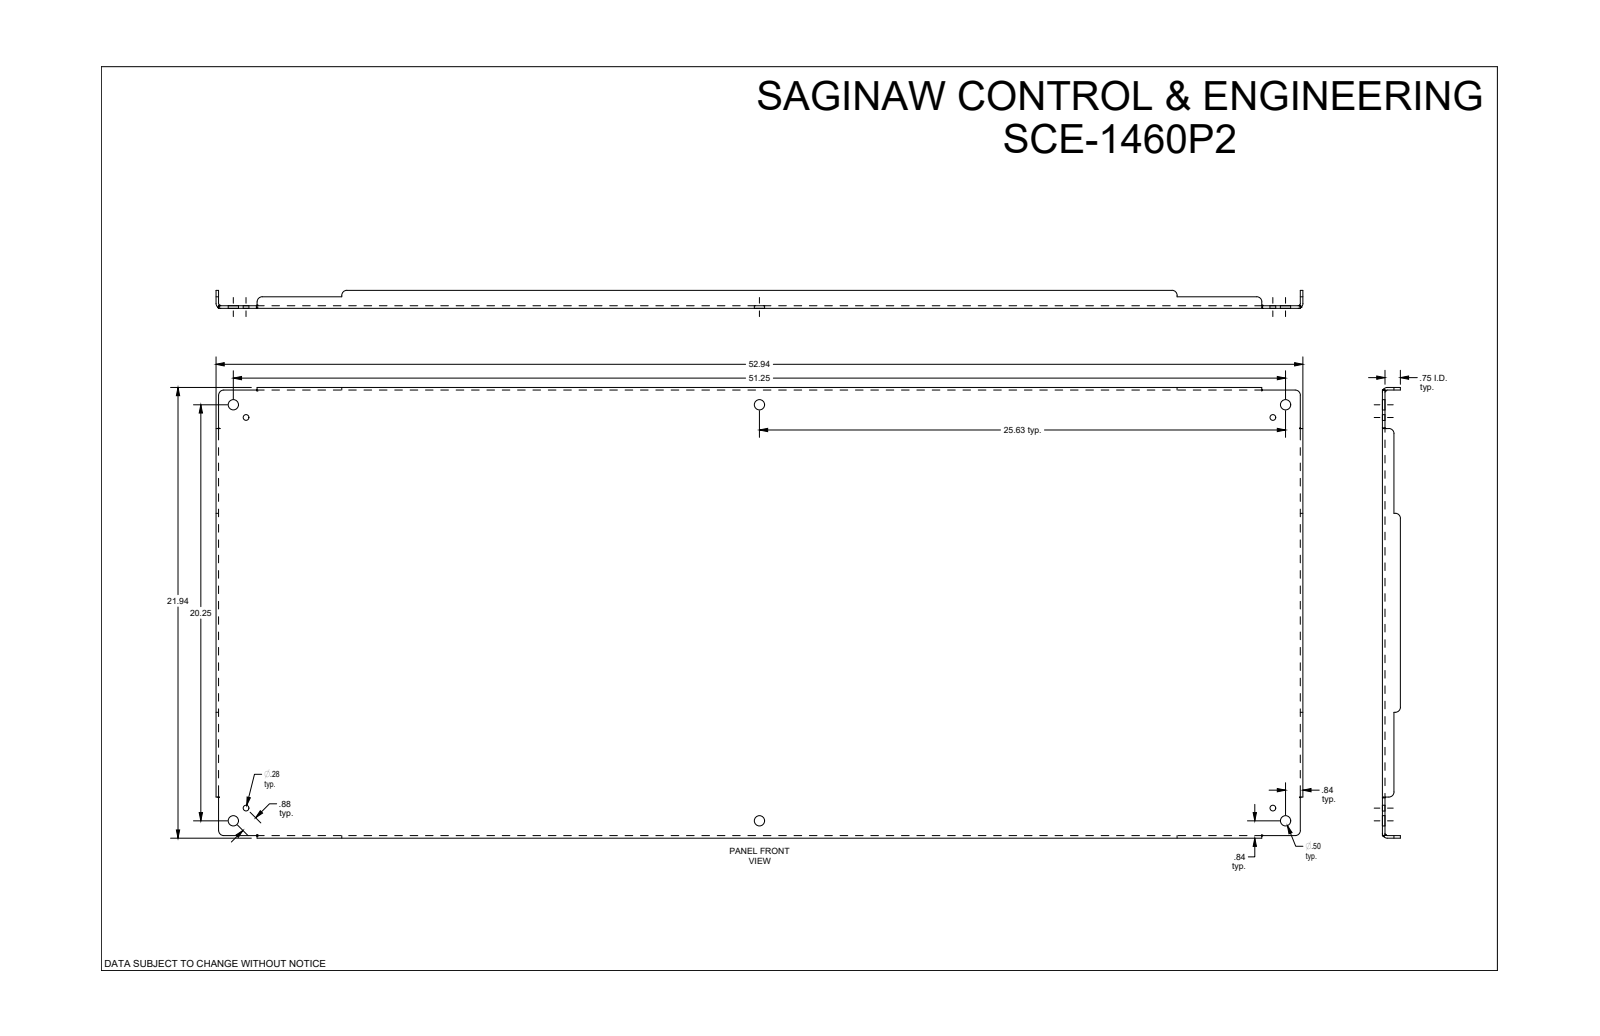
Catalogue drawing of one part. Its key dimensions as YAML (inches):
part_name: "SCE-1460P2"
step_written_by: "SolidWorks 2019 (CONFIG_CONTROL_DESIGN)"
units: inches
bodies: {solids: 1, faces: 108, planar: 46, cylindrical: 38, other: 24}
overall_size: [52.938, 21.938, 0.875]
volume: 154.7
surface_area: 2496
round_holes:
  - {diameter: 0.5, count: 6}
  - {diameter: 0.281, count: 4}
partial_cylinders:
  - {radius: 0.25, count: 12}
  - {radius: 0.112, count: 4}
  - {radius: 0.237, count: 4}
face_to_face_distances: [0.125, 0.125, 21.813, 21.687, 21.938, 52.813, 0.75, 0.875, 52.687, 52.938]
hole_center_spacings: [0.875, 19.641, 25.014, 25.625, 31.792, 32.661, 50.635, 54.304]
